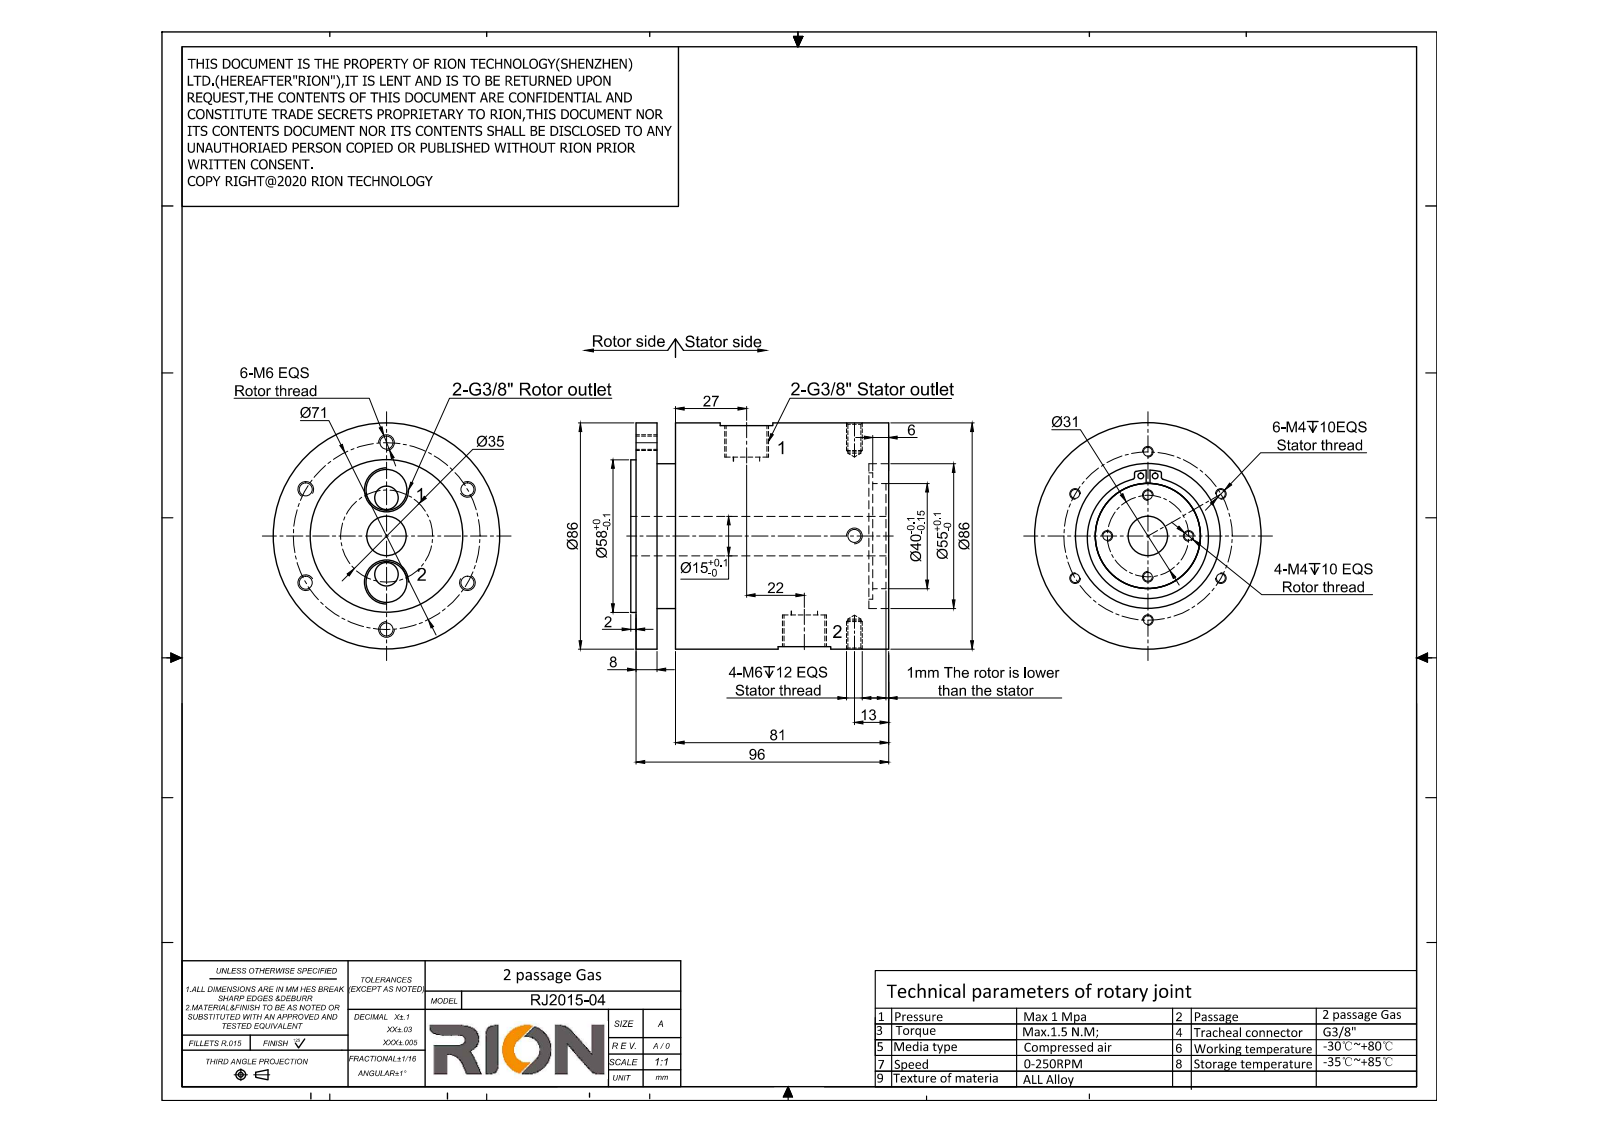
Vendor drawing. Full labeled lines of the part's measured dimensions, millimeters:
Part name (STEP PRODUCT): GJ2015-04
STEP written by: SolidWorks 2014 (CONFIG_CONTROL_DESIGN)
Units: millimetres
Bodies: 1 solid, 123 faces (17 planar, 70 cylindrical, 36 other)
Overall size (bounding box): 98 × 86 × 86
Volume: 499 597 mm³ · Surface area: 55 379 mm²
Round holes (diameter × count): ⌀3.3 ×10, ⌀5 ×8, ⌀9 ×4, ⌀15.25 ×4, ⌀15 ×1, ⌀55 ×1
Round bosses / shafts (diameter × count): ⌀86 ×1, ⌀58 ×1, ⌀40 ×1
Main face-to-face distances: 81, 7, 88, 8, 15, 96, 10, 2, 17, 98
Hole centre spacings: 32, 35.5, 58.48, 27.75, 33.88, 3.5, 55.42, 14.5
